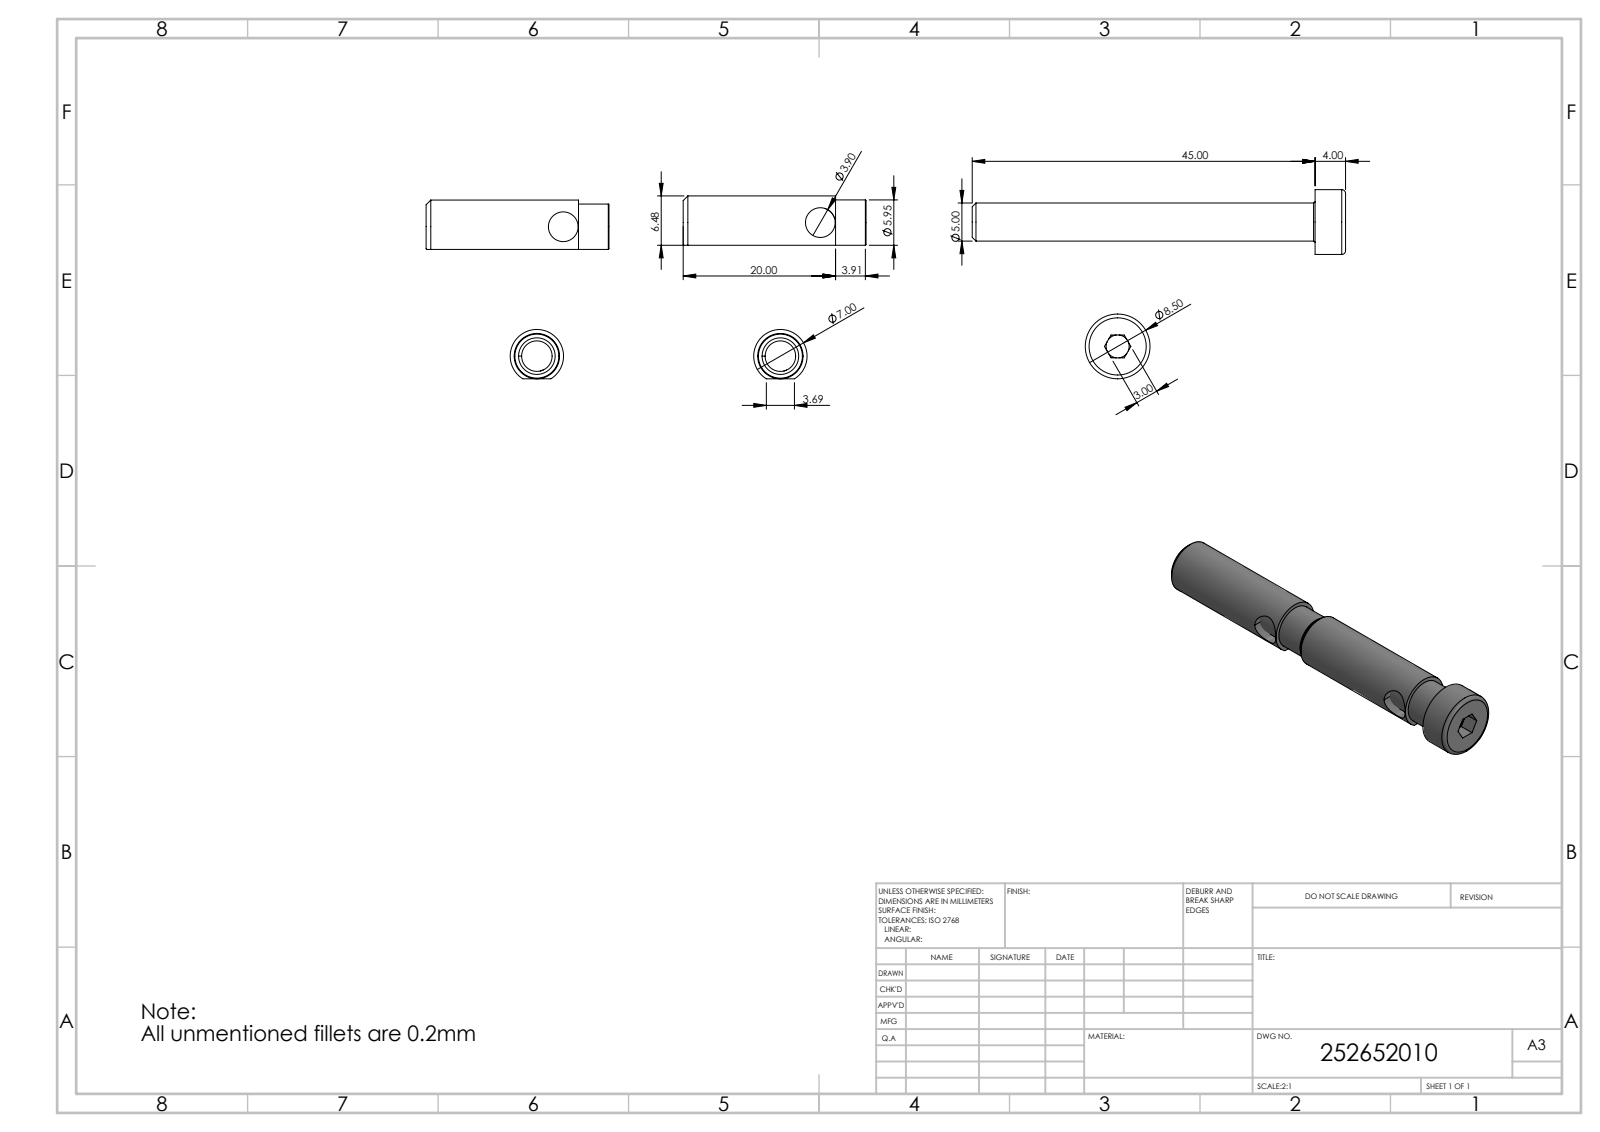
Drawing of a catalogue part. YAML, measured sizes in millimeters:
part_name: "252652010_Automatik_Stoss_Verbinder_set_Shrinkwrap_1"
step_written_by: "Autodesk Inventor 2019 (AUTOMOTIVE_DESIGN)"
units: millimeters
bodies: {solids: 3, faces: 77, planar: 53, cylindrical: 12, other: 12}
overall_size: [52, 8.5, 8.5]
volume: 2092
surface_area: 2631
round_holes:
  - {diameter: 3.9, count: 2}
  - {diameter: 4, count: 1}
round_bosses_or_shafts:
  - {diameter: 8.5, count: 1}
  - {diameter: 7, count: 1}
  - {diameter: 5.95, count: 1}
  - {diameter: 5, count: 1}
face_to_face_distances: [4, 24, 0.98, 4.98, 28, 0.5, 3.5, 3, 20, 21]
hole_center_spacings: [24]
